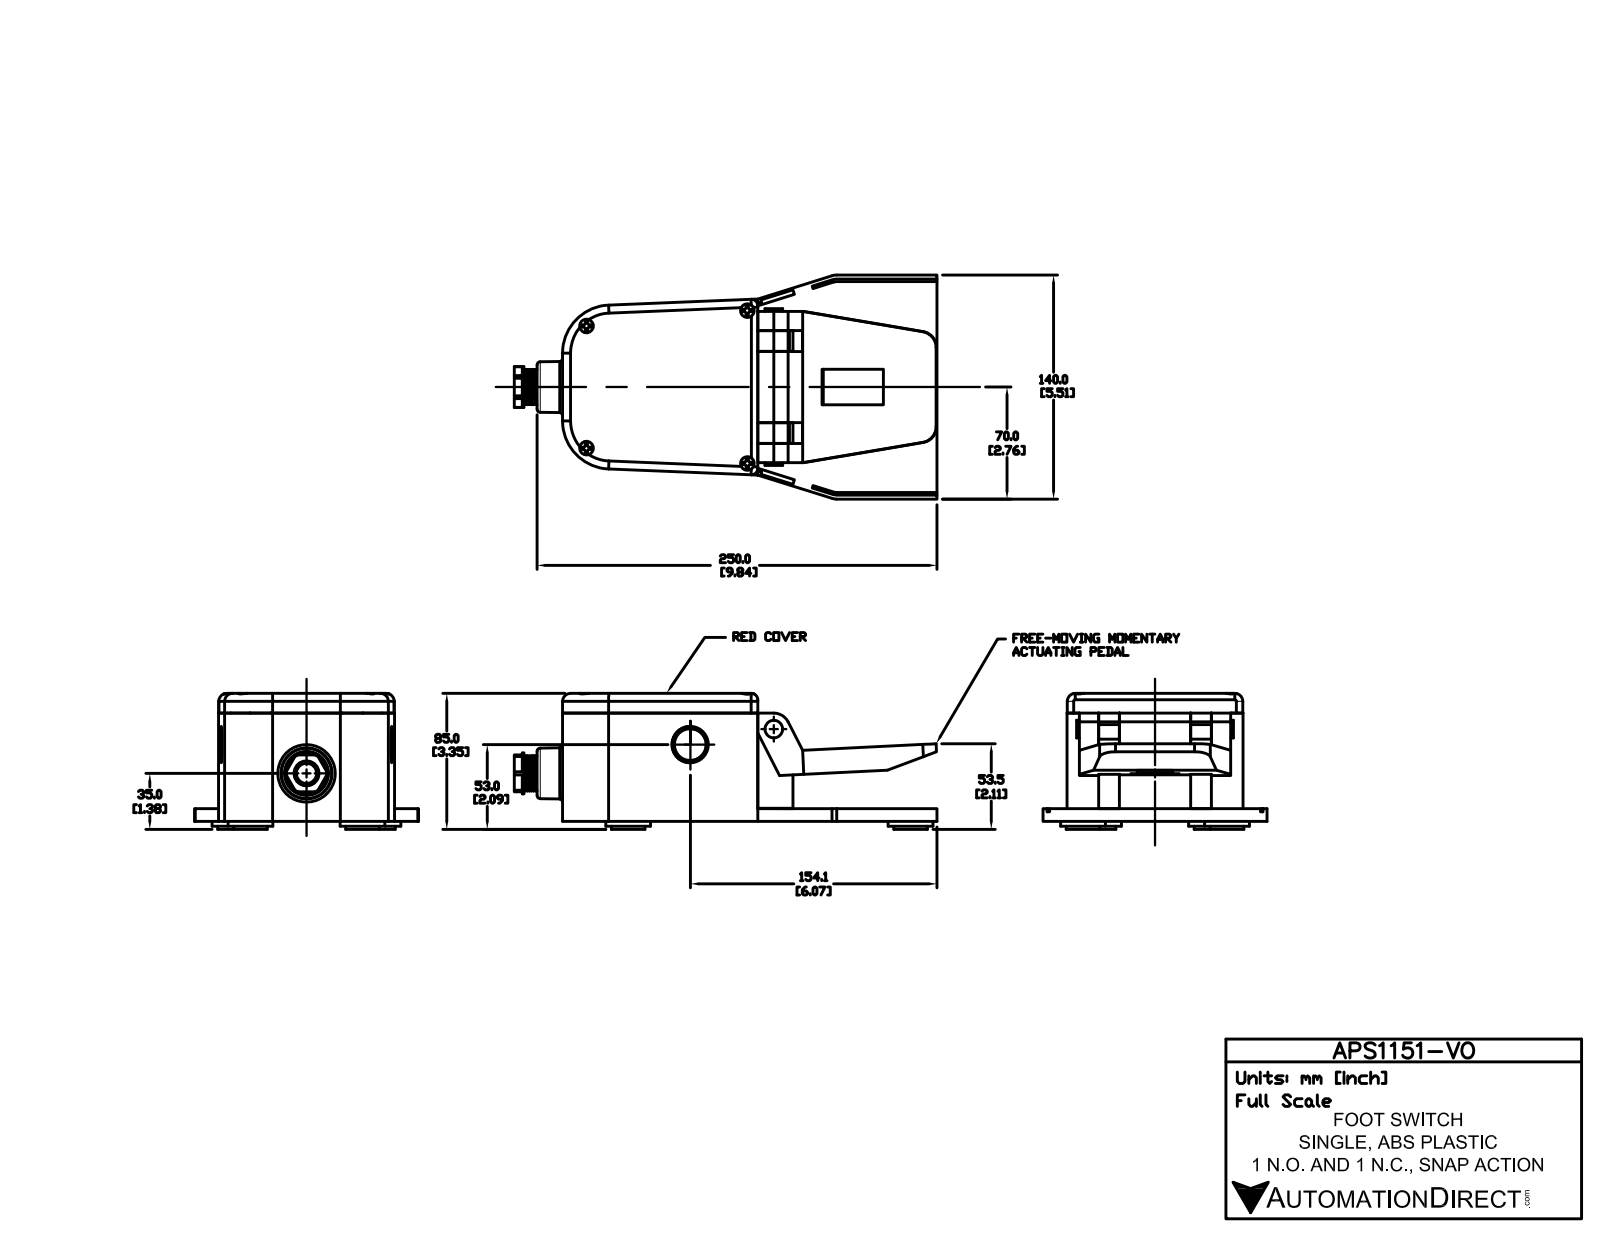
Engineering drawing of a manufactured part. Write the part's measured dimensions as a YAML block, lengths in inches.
part_name: "APS1151-V0"
step_written_by: "SolidWorks 2015 (AUTOMOTIVE_DESIGN)"
units: inches
bodies: {solids: 18, faces: 340, planar: 206, cylindrical: 90, other: 44}
overall_size: [10.404, 5.512, 3.346]
volume: 79.64
surface_area: 268.3
round_holes:
  - {diameter: 0.335, count: 4}
  - {diameter: 0.896, count: 2}
  - {diameter: 0.498, count: 1}
  - {diameter: 0.614, count: 1}
round_bosses_or_shafts:
  - {diameter: 1.102, count: 4}
  - {diameter: 0.827, count: 4}
  - {diameter: 0.782, count: 2}
  - {diameter: 1.004, count: 1}
  - {diameter: 0.433, count: 1}
partial_cylinders:
  - {radius: 0.039, count: 16}
  - {radius: 0.394, count: 5}
  - {radius: 0.157, count: 3}
  - {radius: 0.197, count: 3}
  - {radius: 0.232, count: 2}
  - {radius: 0.295, count: 2}
  - {radius: 1.181, count: 2}
  - {radius: 0.787, count: 1}
face_to_face_distances: [0.315, 2.664, 2.349, 2.663, 2.348, 3.15, 2.835, 0.487, 0.485, 0.591]
hole_center_spacings: [3.976, 5.206, 3.004, 3.76]
